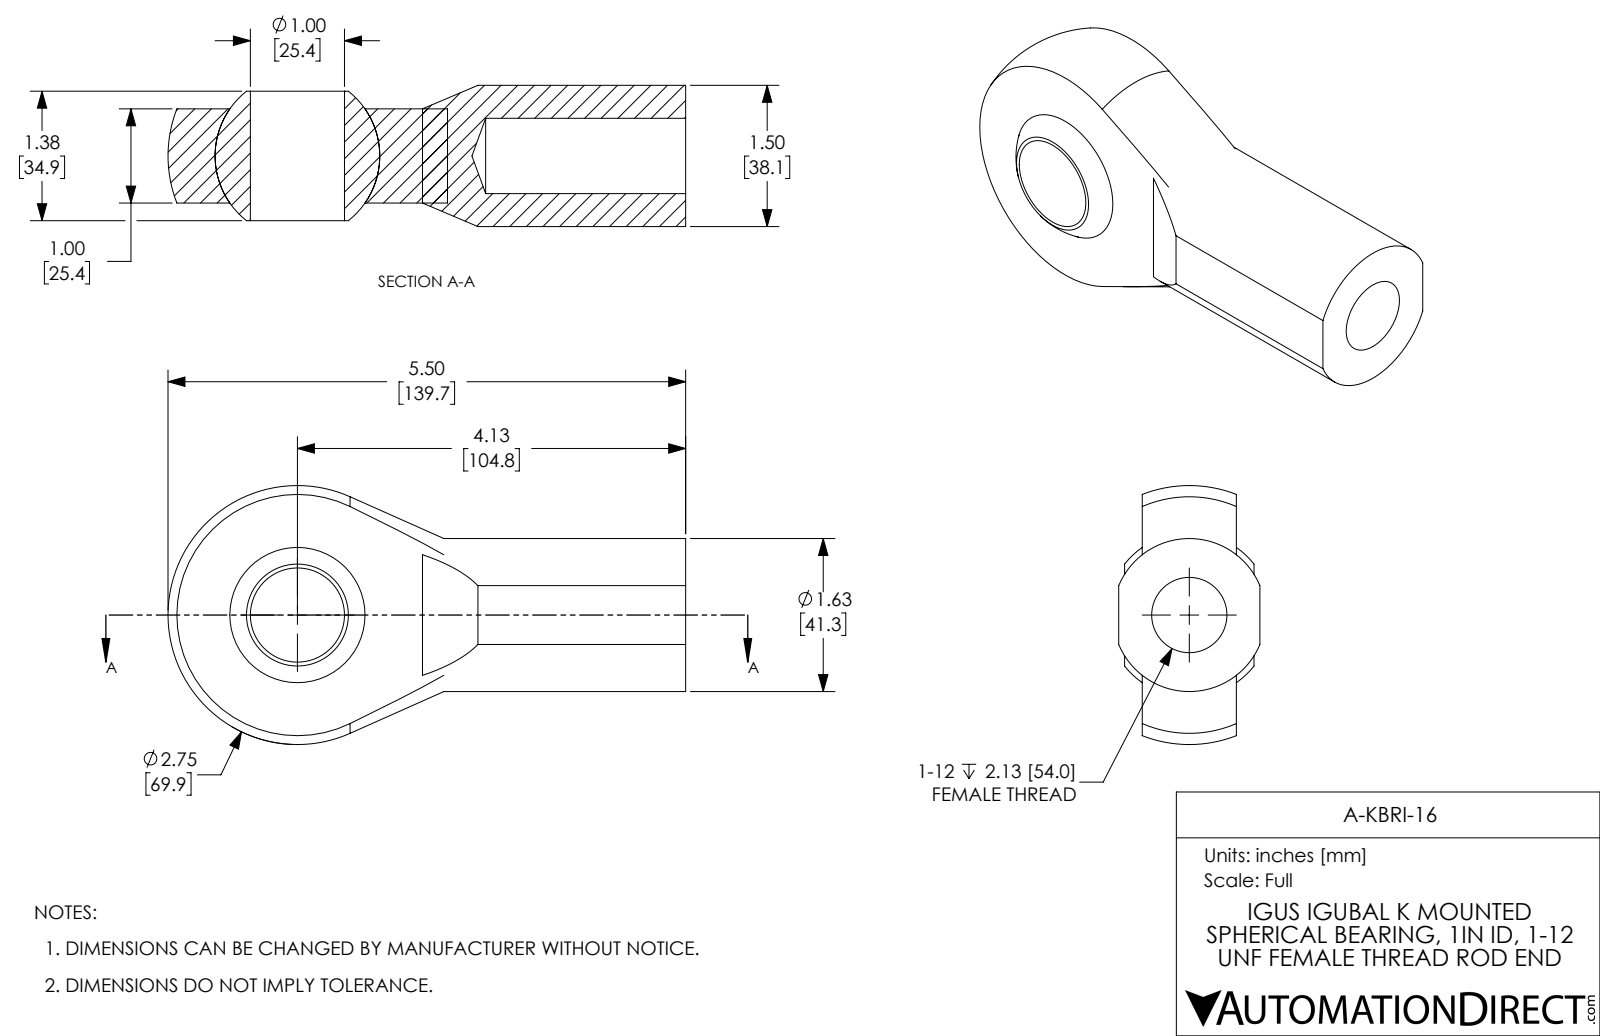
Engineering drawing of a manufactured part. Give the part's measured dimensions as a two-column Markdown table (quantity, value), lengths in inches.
| quantity | value |
| --- | --- |
| part name | A-KBRI-16 |
| STEP written by | SolidWorks 2017 (AUTOMOTIVE_DESIGN) |
| units | inches |
| bodies | 3 solids, 29 faces (11 planar, 7 cylindrical, 11 other) |
| overall size | 5.445 × 2.75 × 1.5 |
| volume | 10.16 in³ |
| surface area | 58.49 in² |
| round holes (diameter × count) | 0.8 × 1, 1 × 1 |
| partial cylindrical surfaces (radius × count) | 0.812 × 1 |
| main face-to-face distances | 1, 0.25, 1.25, 2.796, 2.53, 0.266, 1.5, 0.063, 1.437, 0.187 |
